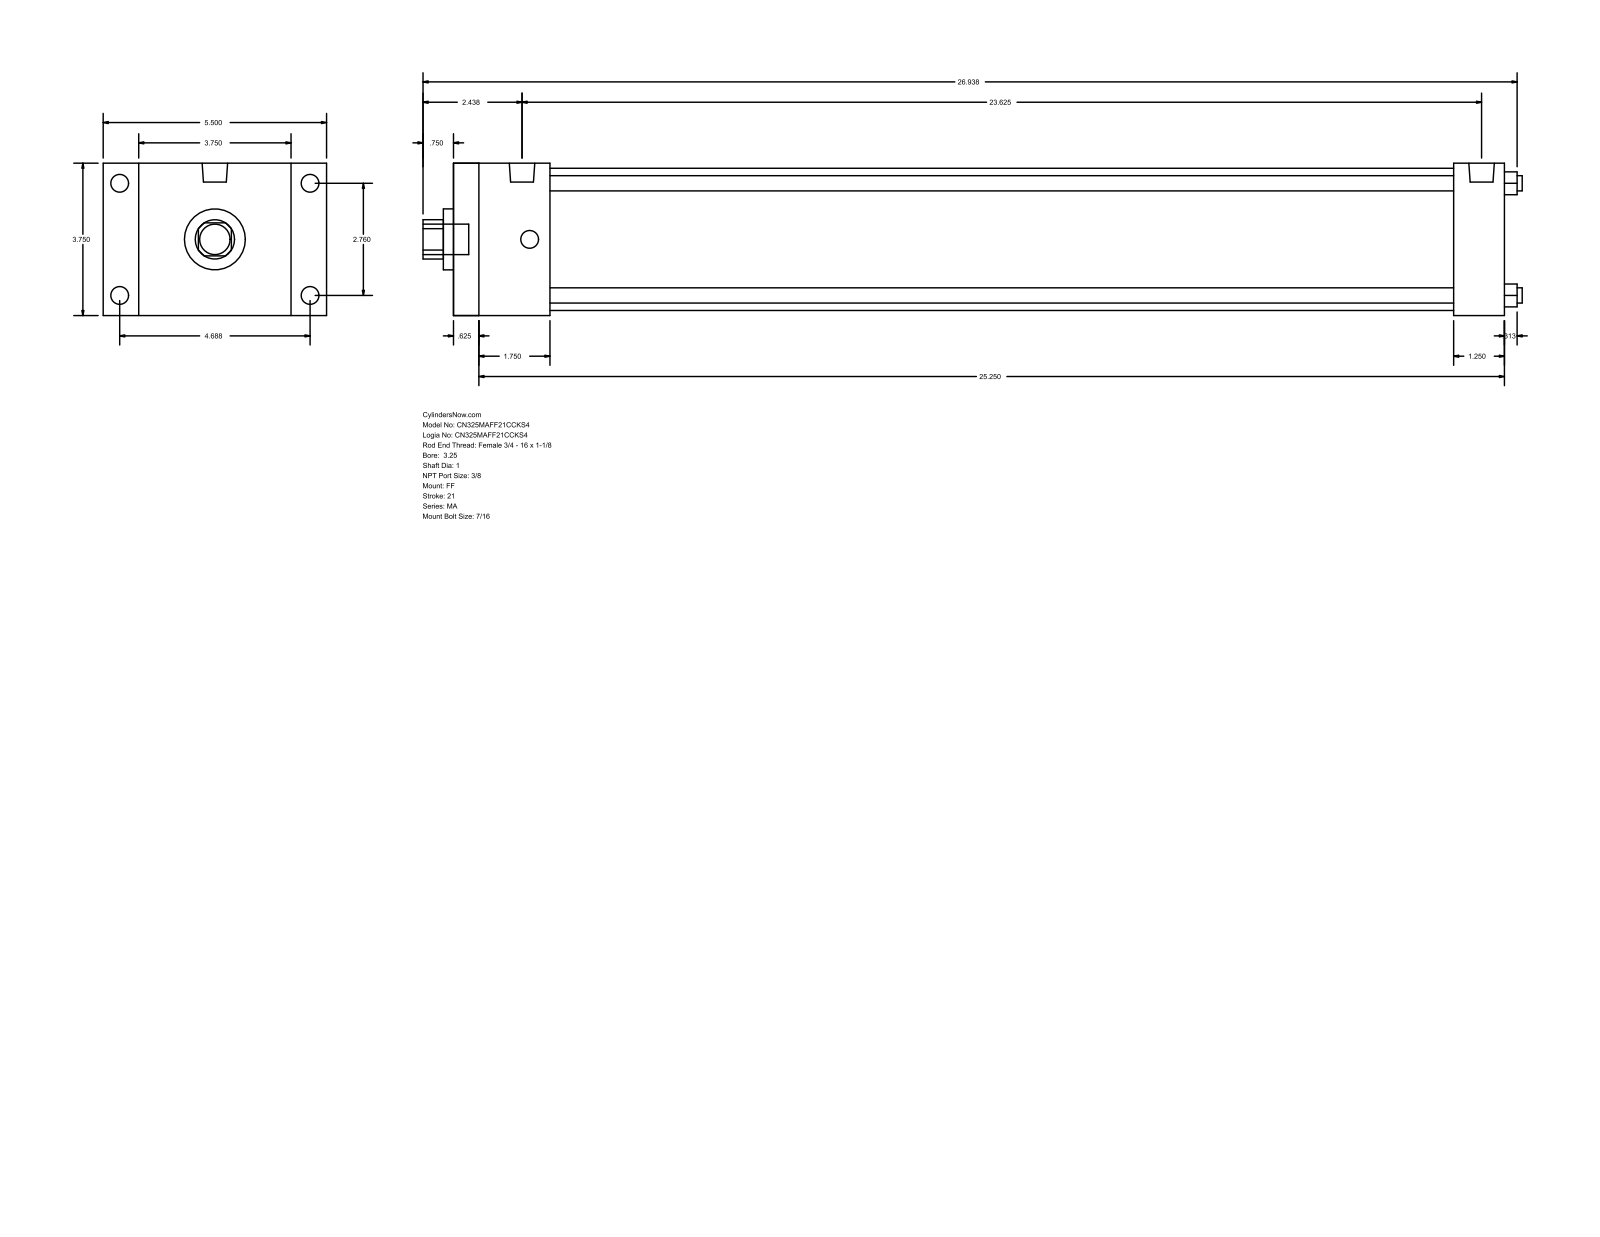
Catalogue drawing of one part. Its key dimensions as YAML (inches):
part_name: "MA_FF__0325_1"
step_written_by: "GSSL Pune (CONFIG_CONTROL_DESIGN)"
units: inches
bodies: {solids: 0, faces: 92, planar: 64, cylindrical: 28, other: 0}
overall_size: [27.063, 5.5, 3.75]
round_holes:
  - {diameter: 0.375, count: 4}
  - {diameter: 1, count: 1}
  - {diameter: 1.5, count: 1}
  - {diameter: 3.5, count: 1}
round_bosses_or_shafts:
  - {diameter: 0.437, count: 8}
  - {diameter: 0.627, count: 2}
  - {diameter: 0.75, count: 1}
partial_cylinders:
  - {radius: 0.484, count: 1}
face_to_face_distances: [3.75, 25.875, 0.625, 25.25, 0.875, 4.625, 2.375, 24.625, 1.75, 24]
hole_center_spacings: [1.952, 2.76, 3.903]
